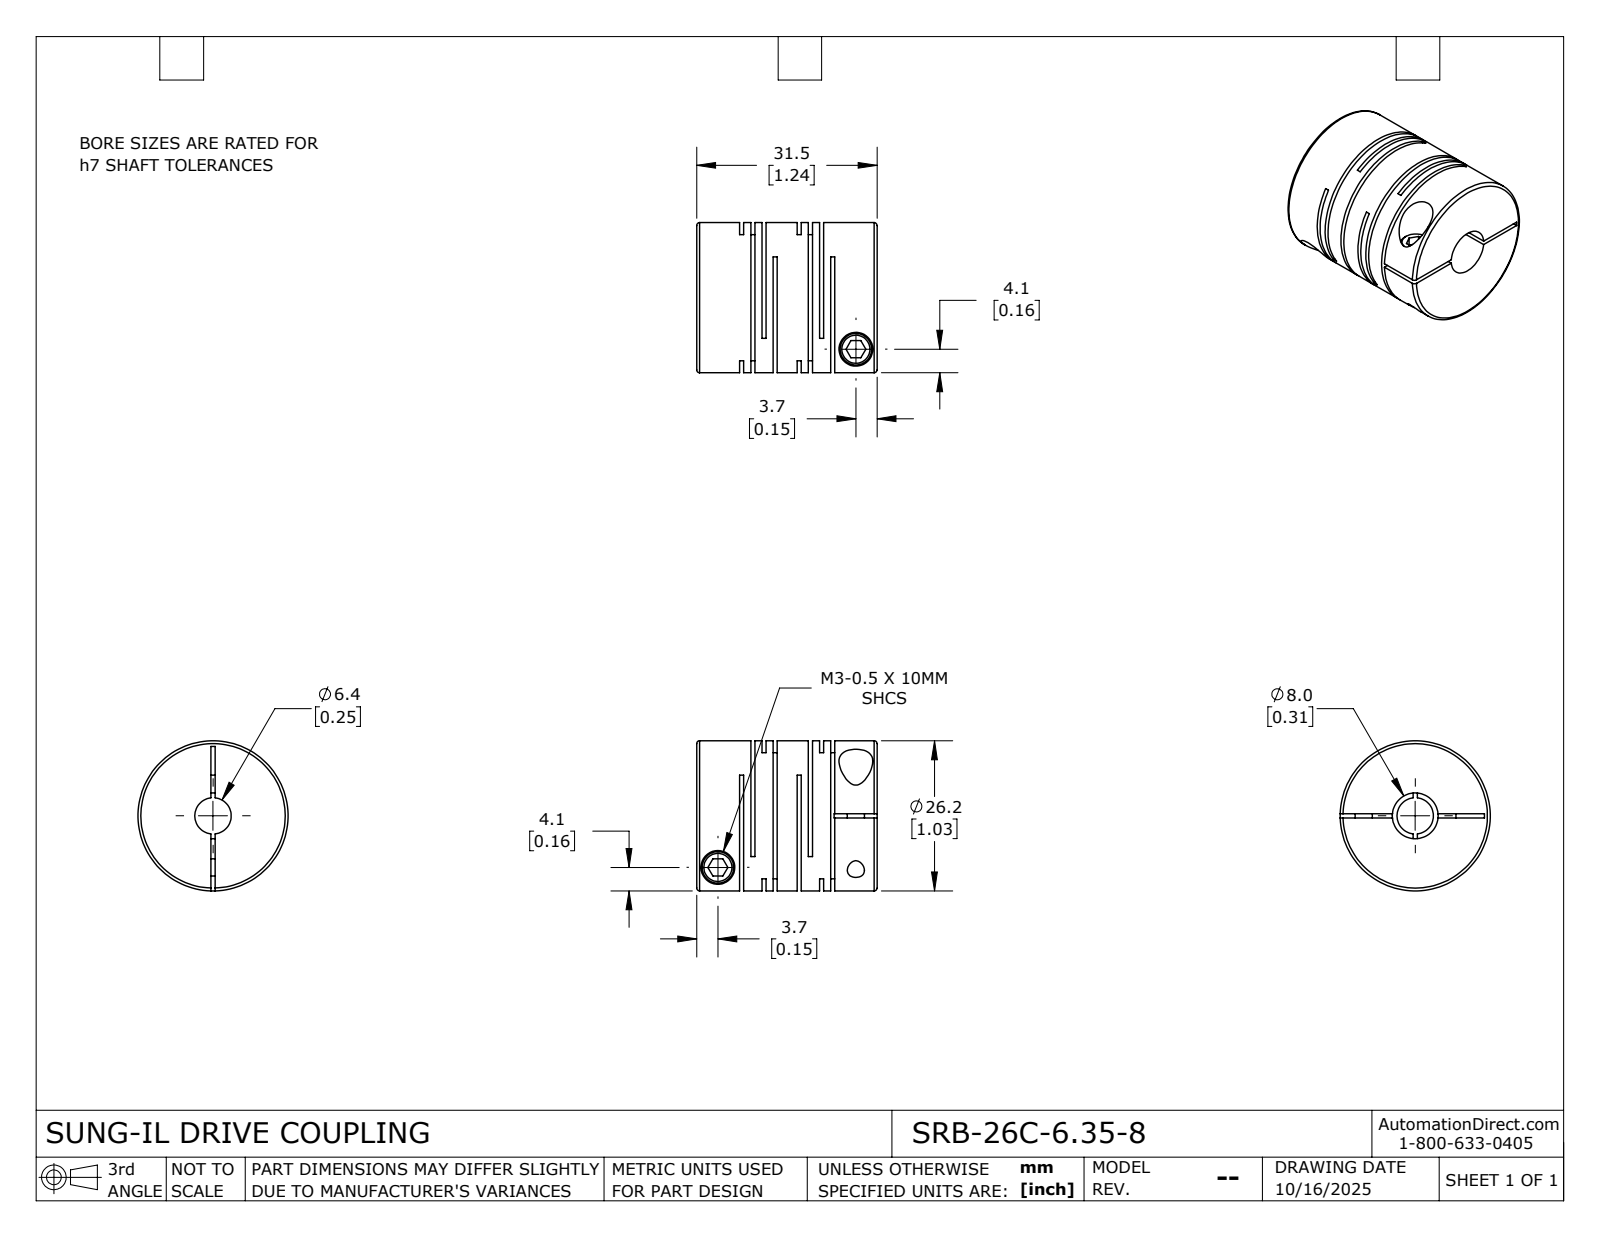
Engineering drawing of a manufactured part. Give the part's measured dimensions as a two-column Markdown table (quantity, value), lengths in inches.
| quantity | value |
| --- | --- |
| part name | SRB-26C-6.35-8 |
| STEP written by | SolidWorks 2024 (CONFIG_CONTROL_DESIGN) |
| units | inches |
| bodies | 1 solid, 115 faces (60 planar, 42 cylindrical, 13 other) |
| overall size | 1.24 × 1.031 × 1.031 |
| volume | 0.78 in³ |
| surface area | 17.27 in² |
| round holes (diameter × count) | 0.118 × 2, 0.232 × 2, 0.25 × 1, 0.315 × 1 |
| round bosses / shafts (diameter × count) | 0.217 × 2, 1.031 × 1 |
| main face-to-face distances | 0.077, 0.396, 0.028, 0.154, 0.319, 0.472, 0.049, 0.105, 0.368, 0.549 |
